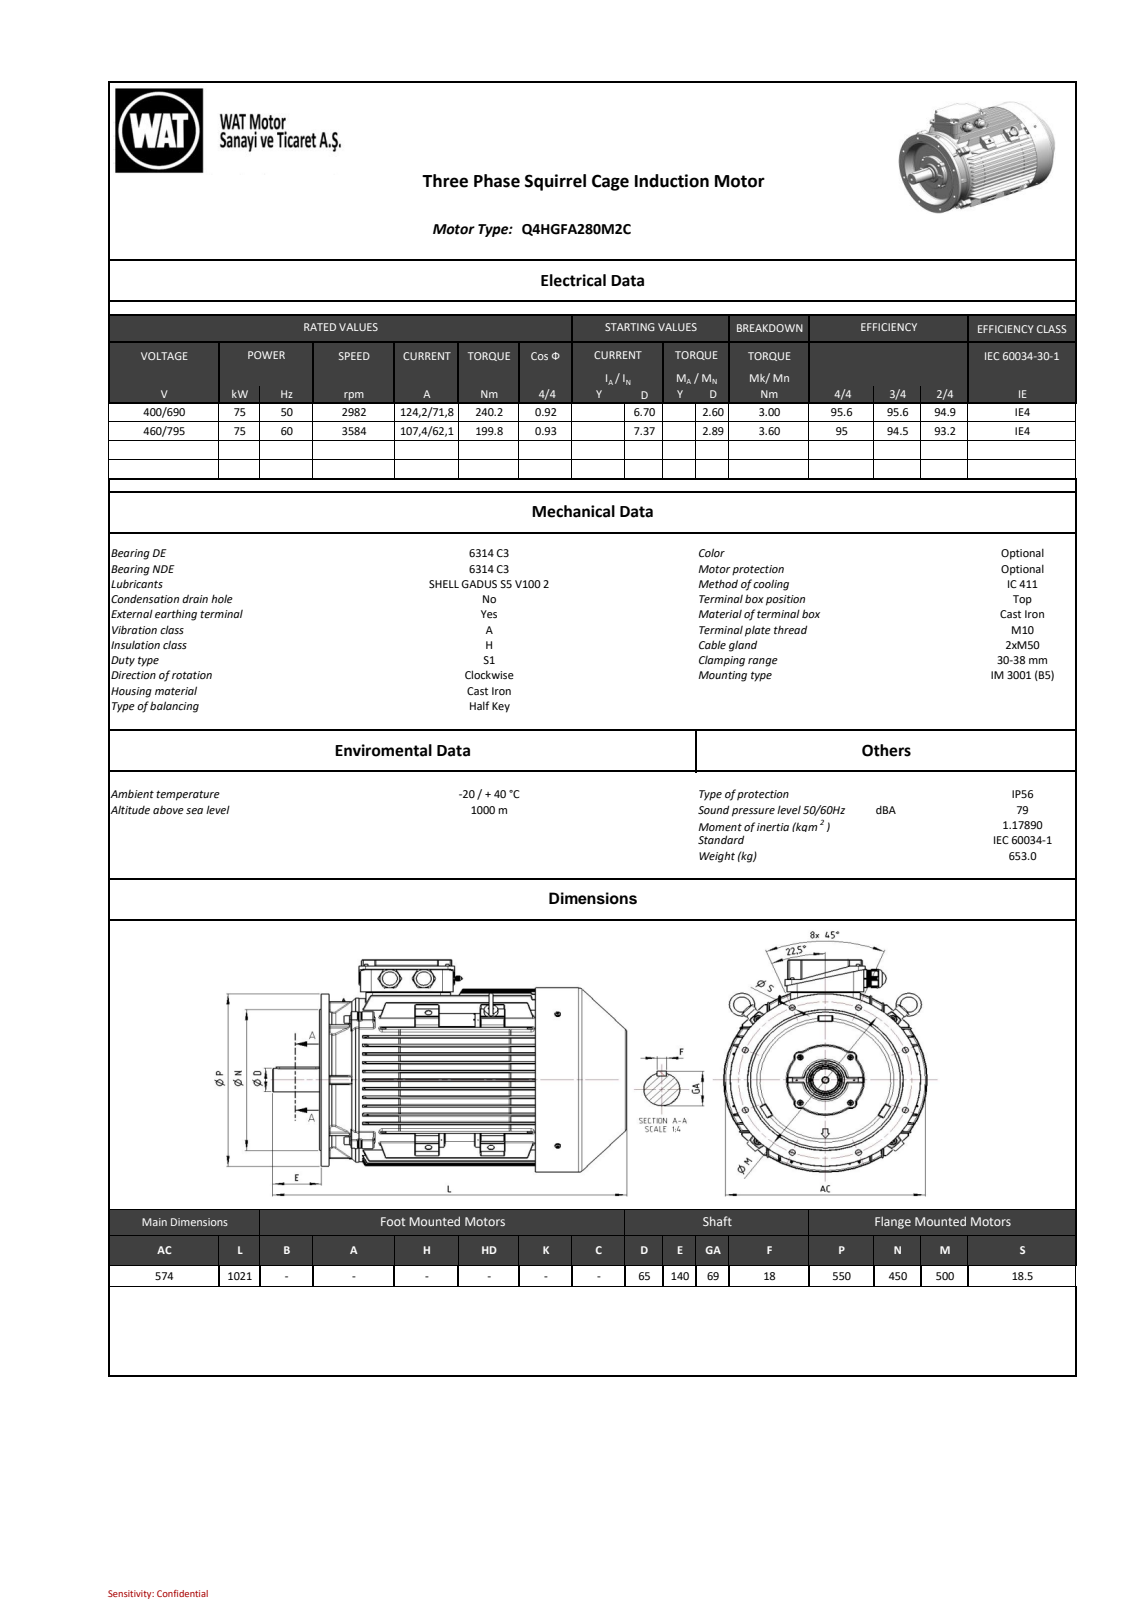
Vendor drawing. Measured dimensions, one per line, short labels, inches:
name: AB_objects
written by: SIEMENS PLM Software NX2206.8101 (AUTOMOTIVE_DESIGN)
unit: in
bodies: 0 solids, 3623 faces (1449 planar, 973 cylindrical, 1201 other)
size: 40.198 × 26.701 × 23.15
holes: 16× ⌀0.728, 4× ⌀0.581, 2× ⌀0.177, 1× ⌀0.394, 1× ⌀0.709, 1× ⌀0.827, 1× ⌀23.031
bosses: 6× ⌀0.63, 4× ⌀1.079, 4× ⌀0.932, 4× ⌀0.619, 4× ⌀0.394, 2× ⌀2.283, 2× ⌀2.169, 2× ⌀2.059
rounds: 341× R0.059, 83× R0.118, 54× R0.039, 24× R0.197, 17× R0.008, 12× R0.079, 12× R0.086, 8× R0.02
face distances: 0.906, 2.323, 1.417, 32.364, 33.781, 34.687, 11.671, 10.32, 9.594, 12.11
hole spacings: 4.122, 7.087, 7.533, 9.843, 11.476, 13.919, 17.144, 18.187
